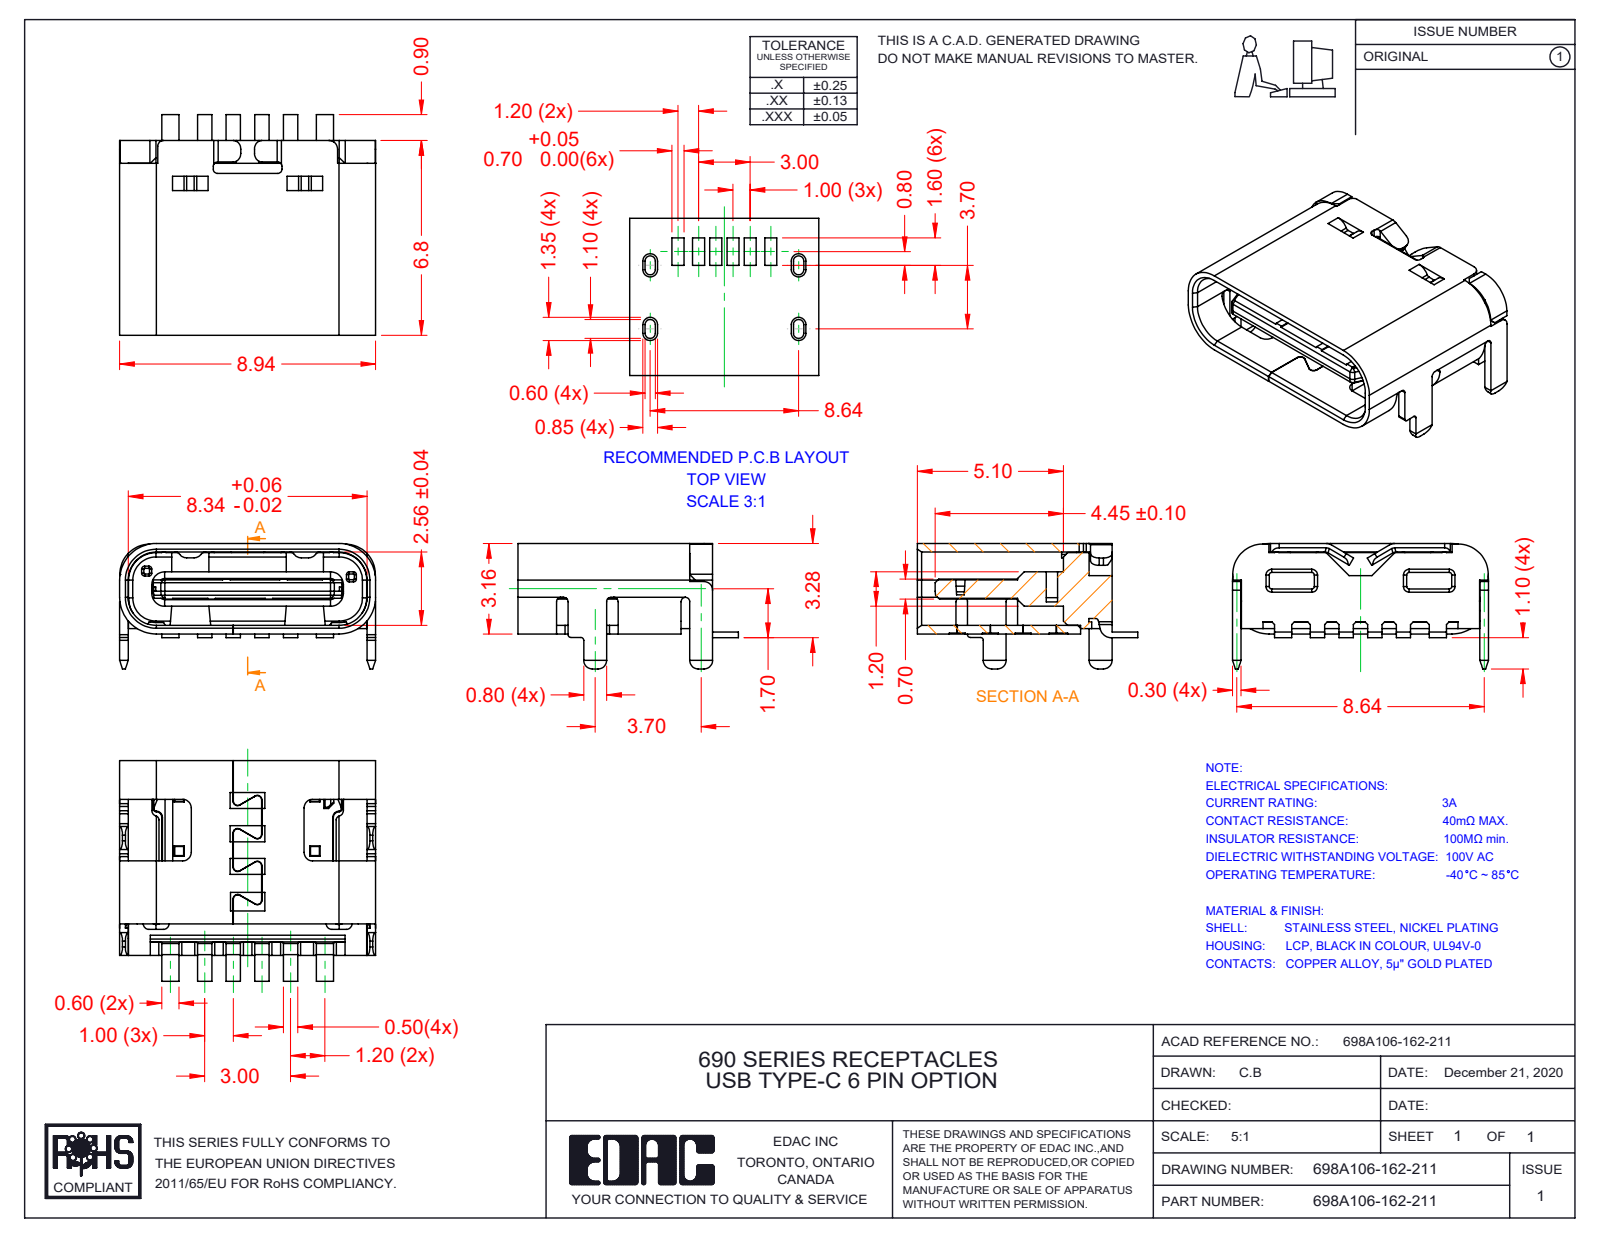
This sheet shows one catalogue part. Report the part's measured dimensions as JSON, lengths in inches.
{"part_name": "Insulator 690A06-162-211; 698A106-162-211 - EDAC USB Connector; Shell 690A106-162-211", "step_written_by": "SolidWorks 2020 (AUTOMOTIVE_DESIGN)", "units": "inches", "bodies": {"solids": 2, "faces": 786, "planar": 595, "cylindrical": 143, "other": 48}, "overall_size": [0.352, 0.303, 0.172], "volume_in3": 0.006, "surface_area_in2": 0.725, "partial_cylinders_radius": [[0.012, 24], [0.004, 21], [0.006, 19], [0.008, 19], [0.006, 8], [0.018, 8], [0.038, 4], [0.039, 4]], "face_to_face_distances": [0.113, 0.101, 0.124, 0.037, 0.026, 0.074, 0.063, 0.038, 0.036, 0.34]}
